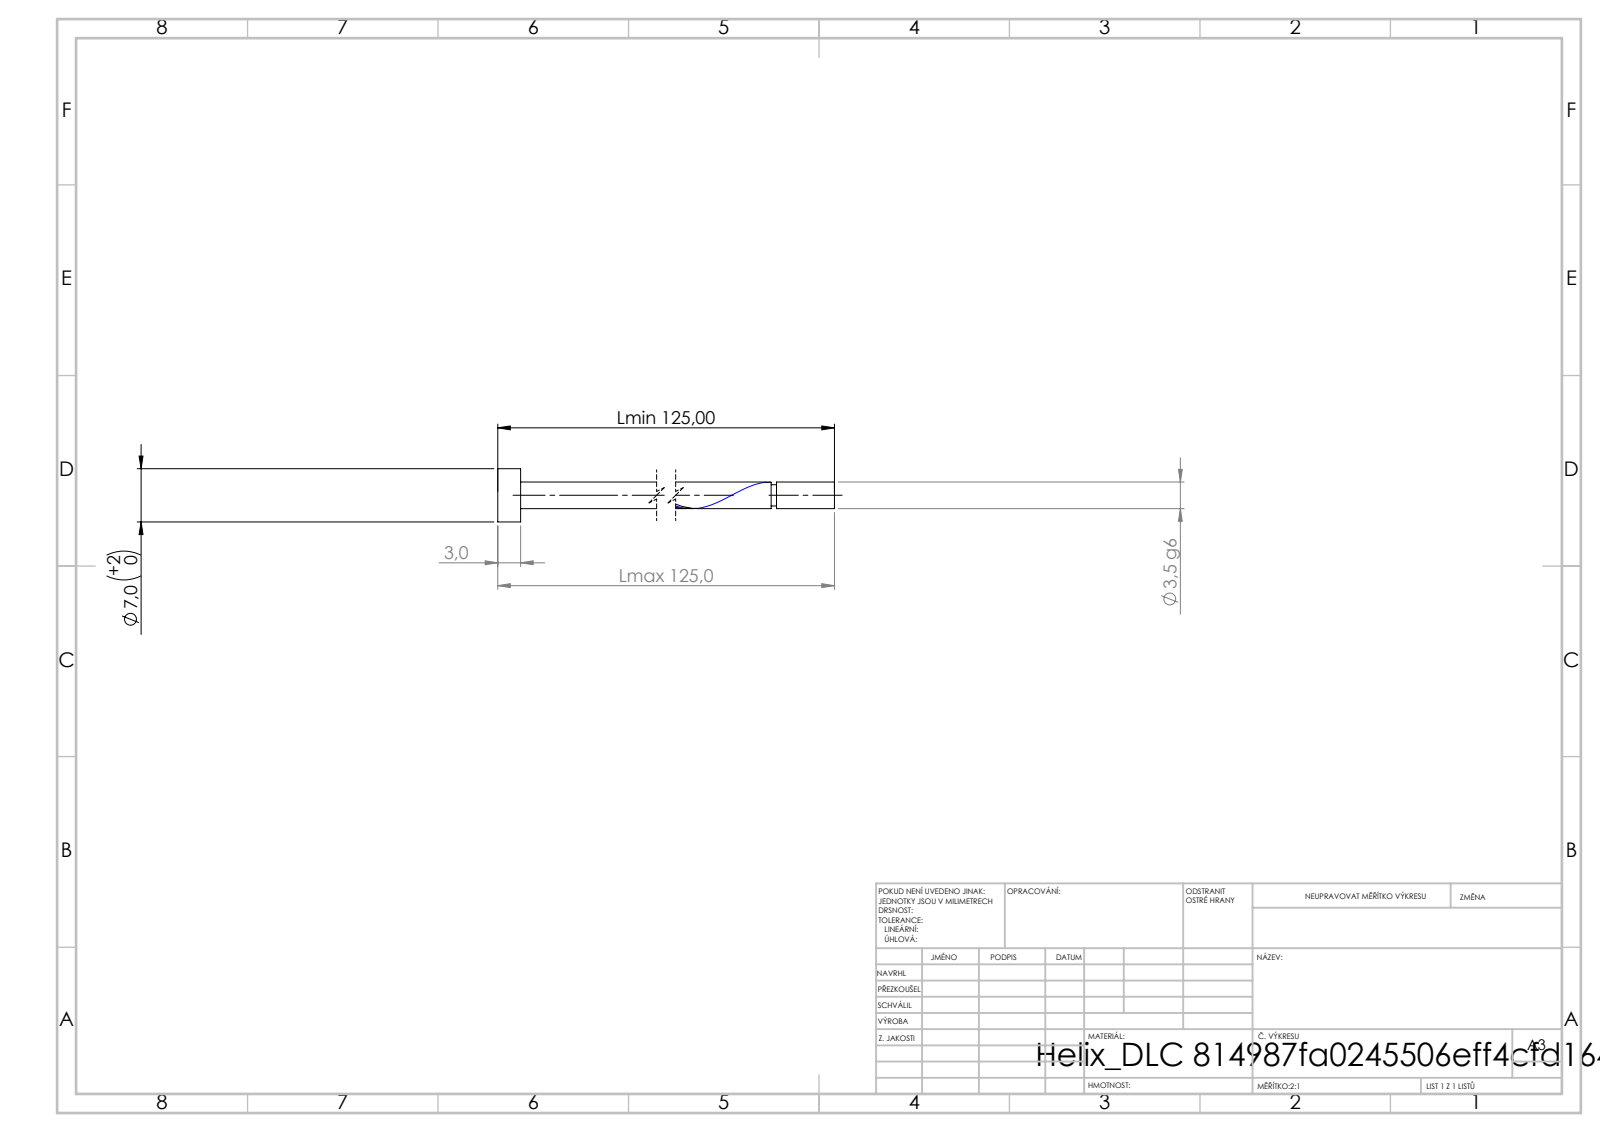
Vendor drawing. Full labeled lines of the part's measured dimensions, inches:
STEP written by: SolidWorks 2019 (CONFIG_CONTROL_DESIGN)
Units: inches
Bodies: 1 solid, 21 faces (6 planar, 14 cylindrical, 1 other)
Overall size (bounding box): 4.921 × 0.276 × 0.276
Volume: 0.078 in³ · Surface area: 2.347 in²
Round bosses / shafts (diameter × count): ⌀0.276 ×1, ⌀0.138 ×1, ⌀0.11 ×1
Main face-to-face distances: 0.118, 4.921, 4.803, 4.622, 4.504, 0.299, 4.594, 4.476, 0.028, 0.327
